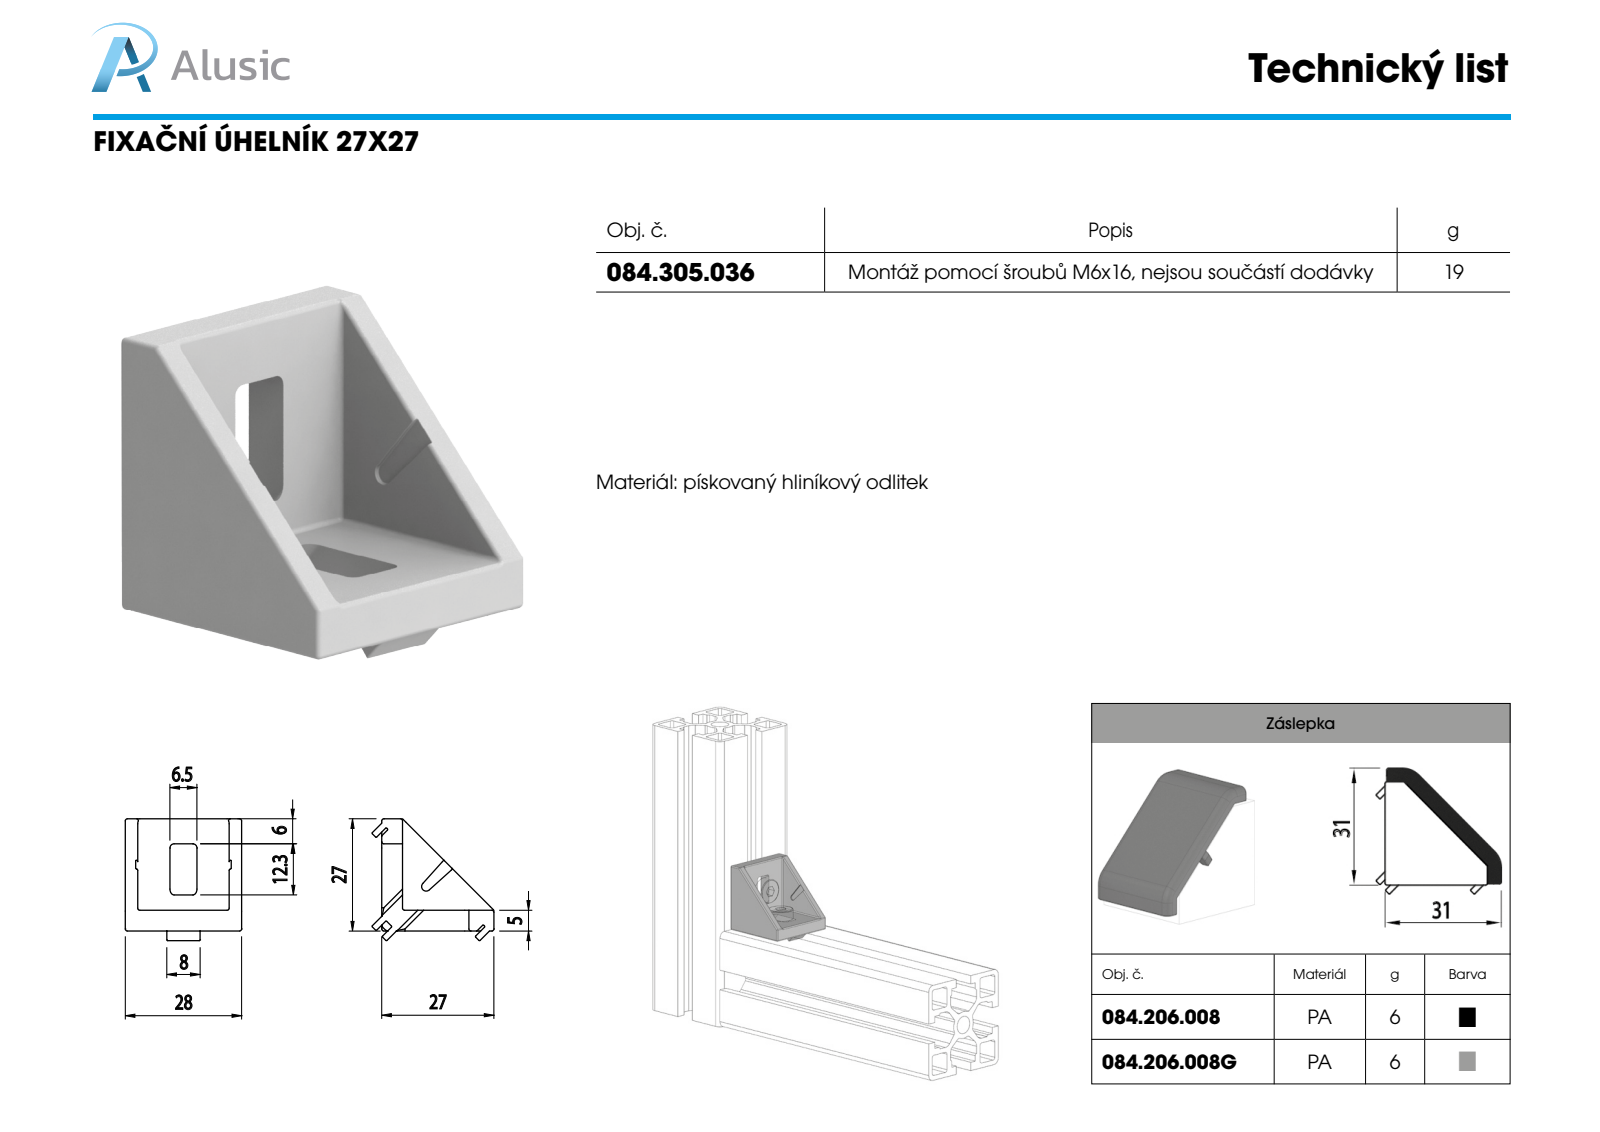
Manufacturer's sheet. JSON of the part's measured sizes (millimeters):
{"part_name": "084.305.036", "step_written_by": "SolidWorks 2016 (CONFIG_CONTROL_DESIGN)", "units": "millimeters", "bodies": {"solids": 1, "faces": 460, "planar": 81, "cylindrical": 203, "other": 176}, "overall_size": [29.32, 29.32, 28], "volume_mm3": 6735, "surface_area_mm2": 4807, "partial_cylinders_radius": [[0.2, 74], [0.5, 44], [1, 21], [0.4, 12], [0.1, 10]], "face_to_face_distances": [5, 28, 3, 22, 25, 7.75, 17.25, 3.3, 1.7, 25.3]}
